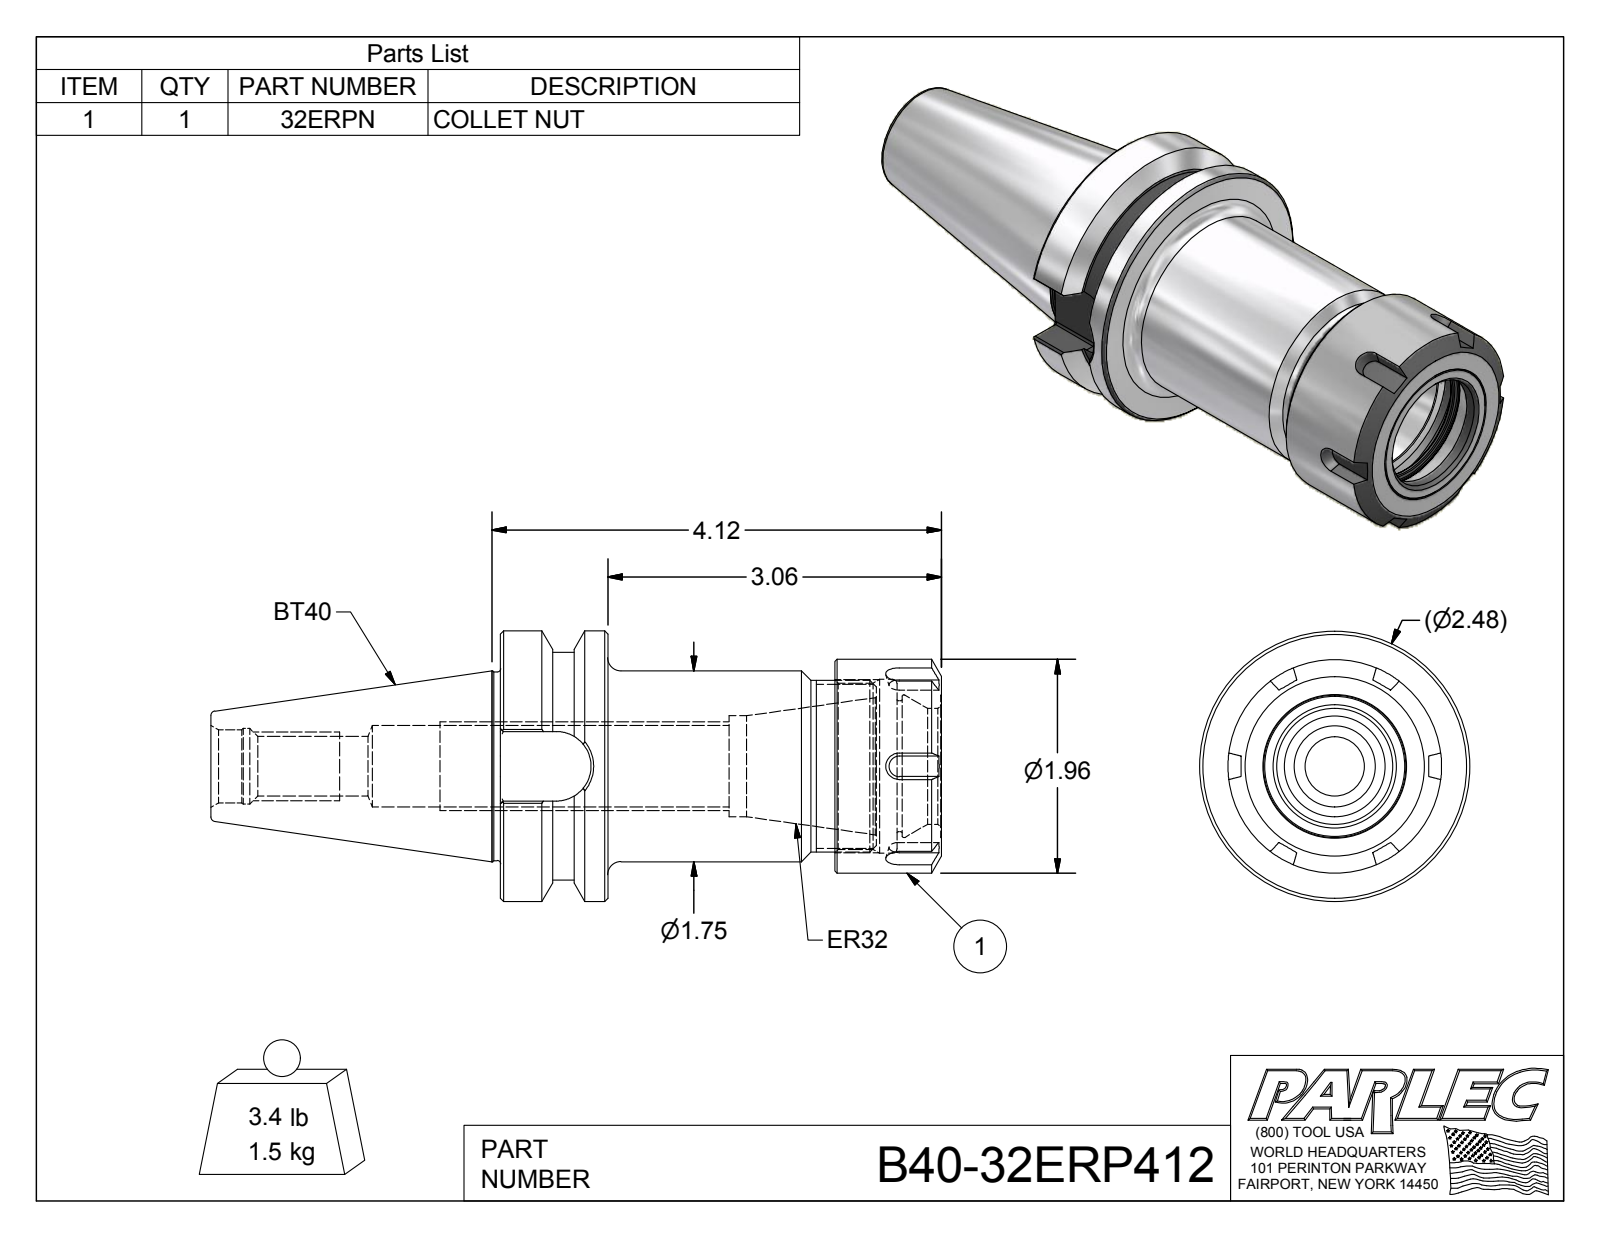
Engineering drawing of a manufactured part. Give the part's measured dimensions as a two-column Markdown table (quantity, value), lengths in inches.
| quantity | value |
| --- | --- |
| part name | B40-32ERP412; B40-32ER4-1; 32ERPN |
| STEP written by | Autodesk Inventor 2012 (AUTOMOTIVE_DESIGN) |
| units | inches |
| bodies | 2 solids, 119 faces (47 planar, 29 cylindrical, 43 other) |
| overall size | 6.695 × 2.48 × 2.48 |
| volume | 11.99 in³ |
| surface area | 69.07 in² |
| round holes (diameter × count) | 0.545 × 1, 0.67 × 1, 0.694 × 1, 0.745 × 1, 0.925 × 1, 1.063 × 1, 1.2 × 1, 1.305 × 1, 1.523 × 1, 1.595 × 1 |
| round bosses / shafts (diameter × count) | 2.48 × 1, 2.087 × 1, 1.958 × 1, 1.75 × 1, 1.73 × 1, 1.575 × 1 |
| partial cylindrical surfaces (radius × count) | 0.02 × 8, 0.319 × 1 |
| main face-to-face distances | 0.984, 4.042, 3.058, 3.064, 2.08, 0.978, 3.635, 2.651, 0.571, 0.407 |
